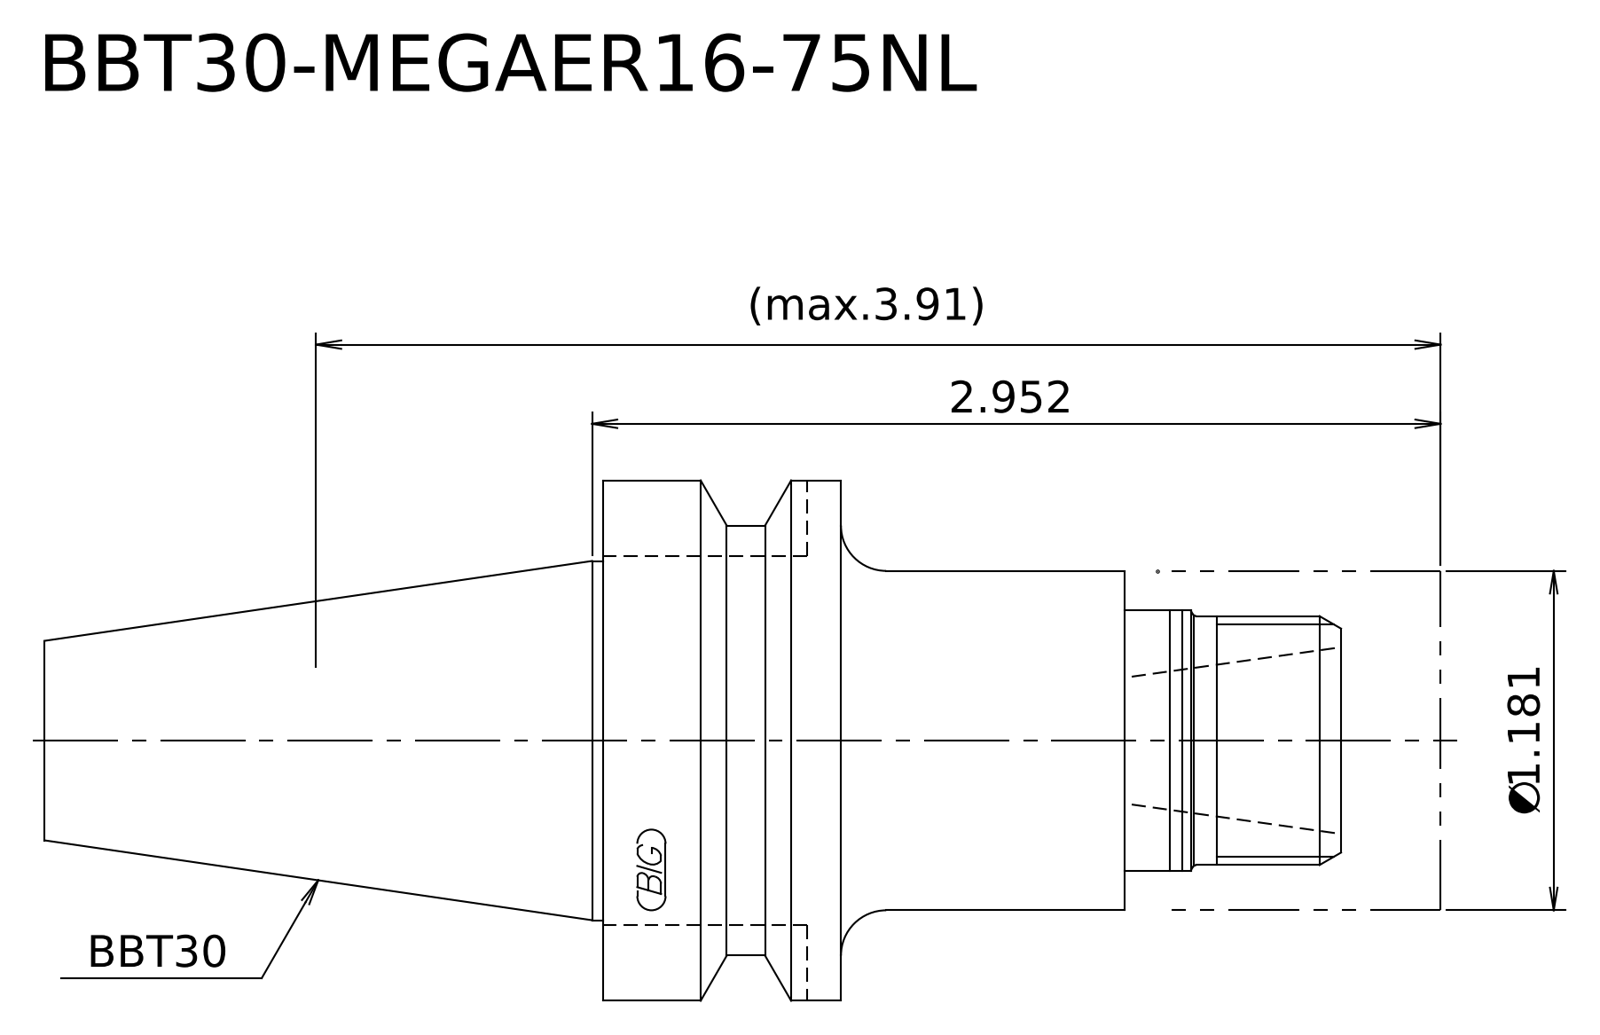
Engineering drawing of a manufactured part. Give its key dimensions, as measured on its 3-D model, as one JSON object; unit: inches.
{"step_written_by": "Kubotek KeyCreator 2011 V10.0.2 (22737) (automotive_design)", "units": "inches", "bodies": {"solids": 2, "faces": 21, "planar": 7, "cylindrical": 8, "other": 6}, "overall_size": [4.858, 1.811, 1.811], "volume_in3": 6.108, "surface_area_in2": 26.93, "round_bosses_or_shafts": [[1.811, 1], [1.496, 1], [1.25, 1], [1.181, 1], [0.906, 1], [0.866, 1]], "face_to_face_distances": [1.929, 0.984, 2.913, 2.087, 1.102, 0.827, 0.346, 0.638, 1.74, 2.567]}
